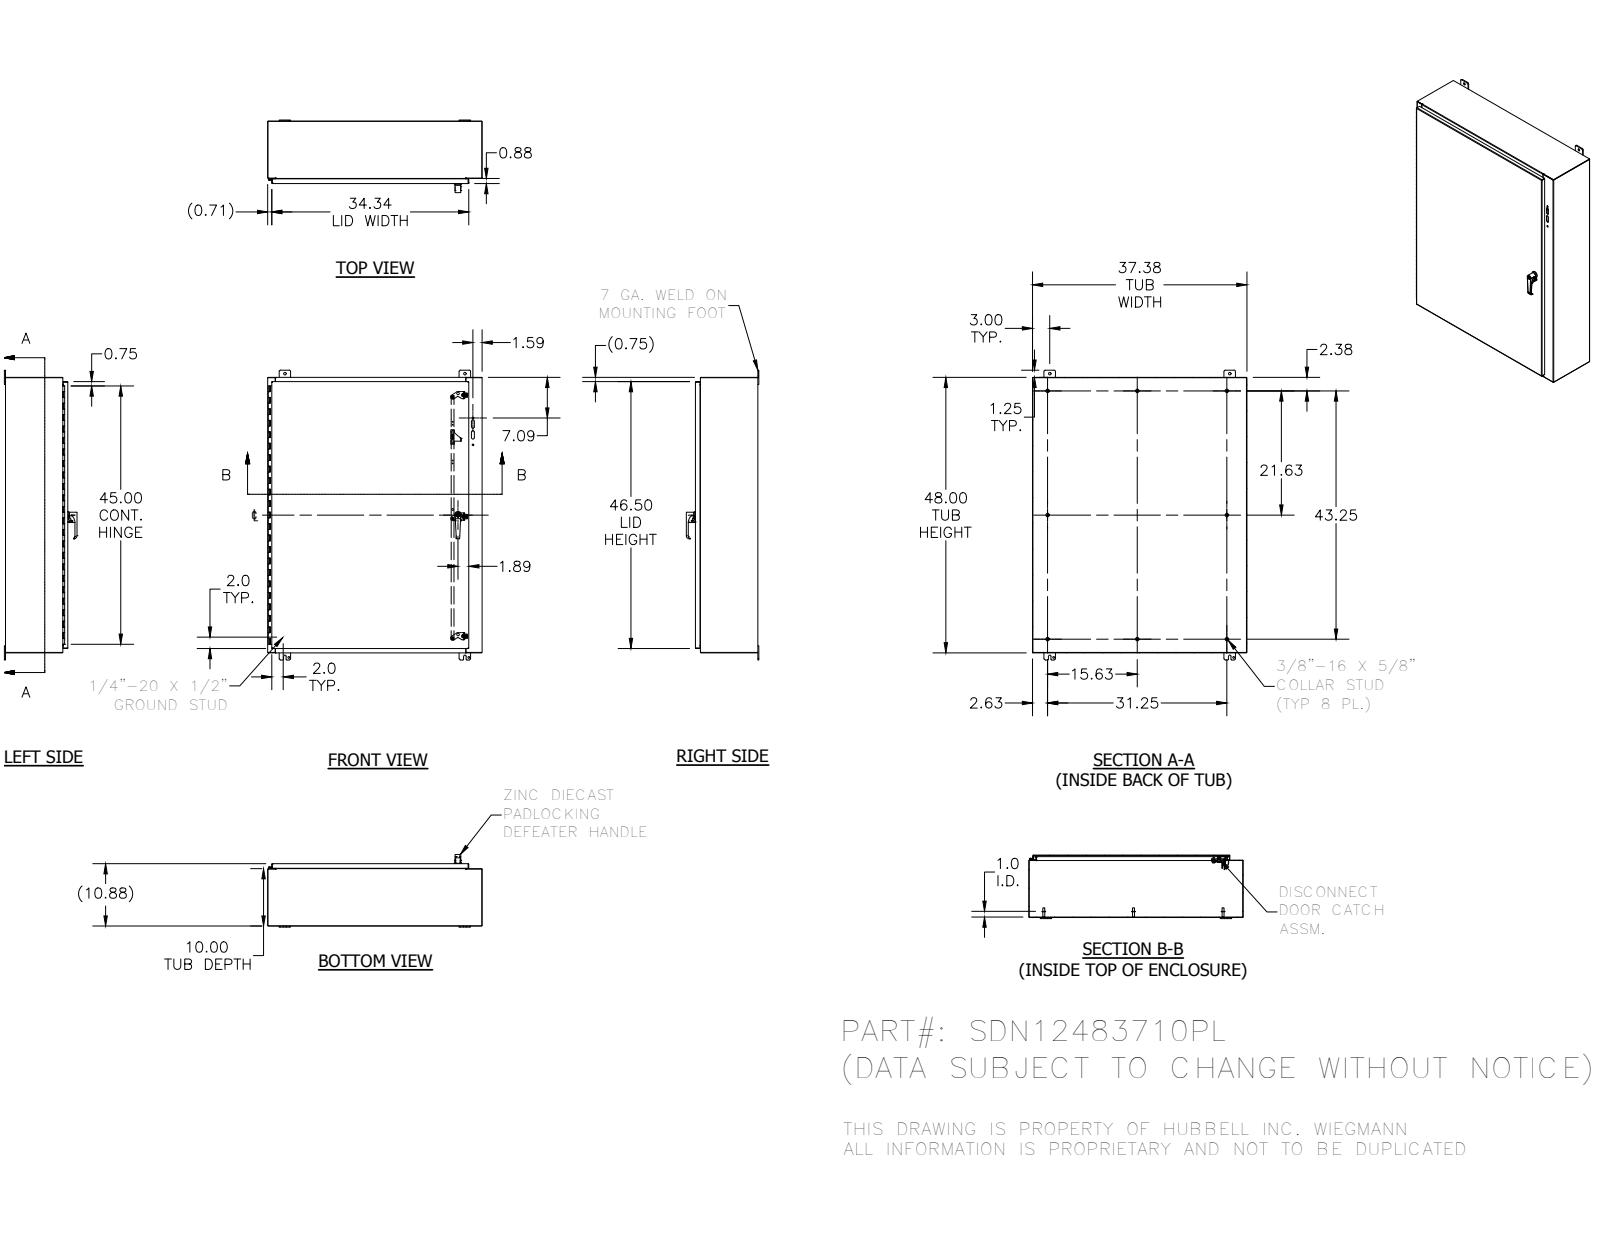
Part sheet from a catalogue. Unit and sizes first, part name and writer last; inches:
Units: inches
Overall size (bounding box): 50.5 × 37.375 × 12.649
Round holes (diameter × count): ⌀0.145 ×6, ⌀0.313 ×4, ⌀0.32 ×4, ⌀0.438 ×4, ⌀0.196 ×3, ⌀0.211 ×3, ⌀0.22 ×3, ⌀0.313 ×3, ⌀0.45 ×3, ⌀0.156 ×2, ⌀0.281 ×2, ⌀0.307 ×2
Round bosses / shafts (diameter × count): ⌀0.625 ×10, ⌀0.33 ×10, ⌀0.437 ×6, ⌀0.3 ×6, ⌀0.225 ×6, ⌀0.25 ×4, ⌀0.19 ×4, ⌀0.75 ×3
Partial cylindrical surfaces — rounded edges, fillets, slot ends (radius × count): R0.02 ×38, R0.012 ×31, R0.025 ×24, R0.25 ×23, R0.031 ×18, R0.105 ×18, R0.125 ×18, R0.094 ×6
Main face-to-face distances: 0.074, 10.801, 10.727, 10.875, 37.301, 47.926, 9.926, 0.875, 37.227, 37.375
Hole centre spacings: 1.593, 31.375, 48, 57.344, 0.5, 20.844, 21.156, 42
Volume: 434.1 in³ · Surface area: 11 649 in²
Bodies: 64 solids, 1889 faces (1012 planar, 623 cylindrical, 254 other)
Part name (STEP PRODUCT): SDN12483710PL; SDN12483710PLBLR; 3889; 34840 (+8 more)
STEP written by: Autodesk Inventor 2012 (AUTOMOTIVE_DESIGN)
